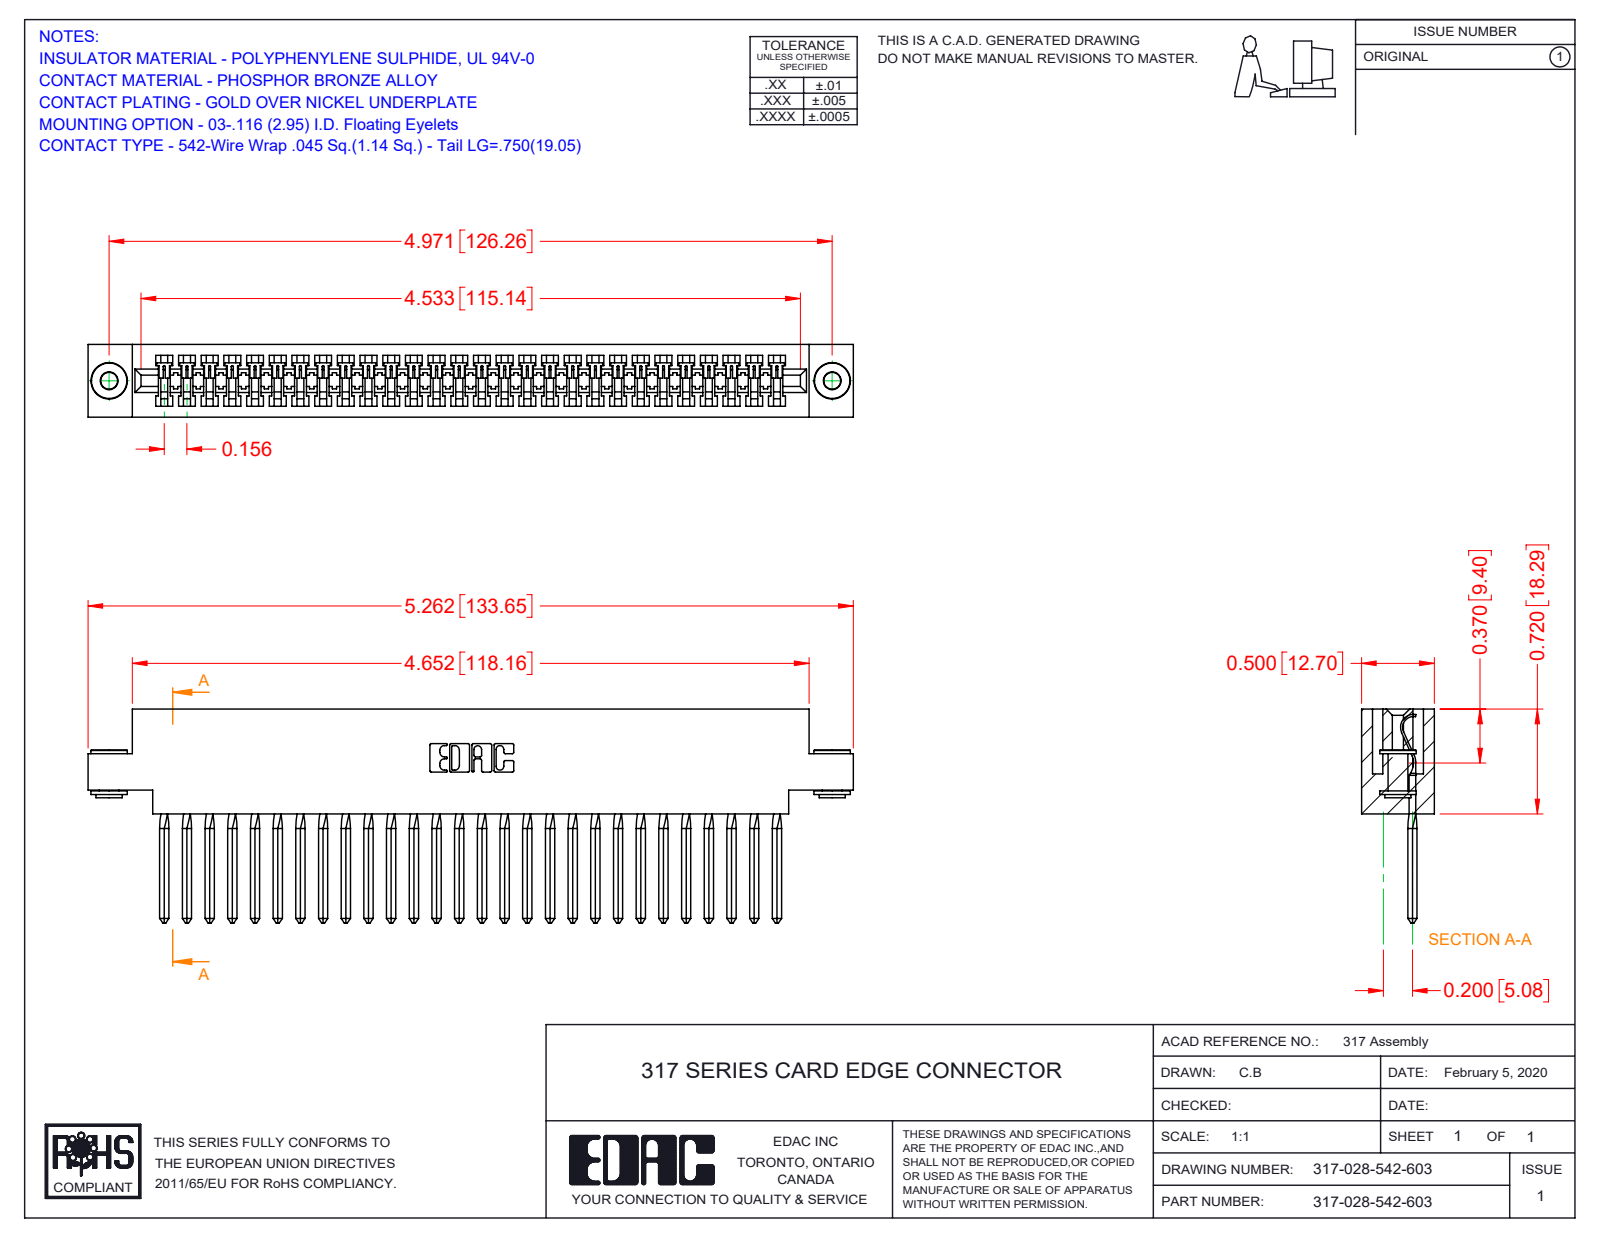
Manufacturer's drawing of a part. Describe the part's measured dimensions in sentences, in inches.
The part is named "317 Part_.156 Dia - TH; 317-028-542-603; 345-250-002_345-250-002-102; 317-290-003_542". Its 3-D file was written by "SolidWorks 2016 (CONFIG_CONTROL_DESIGN)". It is 31 solids with 2240 faces: 1860 planar, 260 cylindrical and 120 other. Overall it measures 5.262 by 1.47 by 0.5 inches. Its volume is 1.238 cubic inches and its surface area 38.23 square inches. Round holes: 2 of diameter 0.116, 2 of diameter 0.156. Round bosses or shafts: 2 of diameter 0.25, 2 of diameter 0.18, 2 of diameter 0.136. Partial cylindrical surfaces (rounded edges, fillets, slot ends): 56 of radius 0.006, 22 of radius 0.01, 6 of radius 0.007, 6 of radius 0.031, 3 of radius 0.026, 1 of radius 0.074, 1 of radius 0.089, 1 of radius 0.1. The main face-to-face distances are 0.5, 0.075, 0.425, 0.35, 0.11, 0.72, 0.136, 0.279, 0.211, 0.289. The hole center spacings are 4.971.
